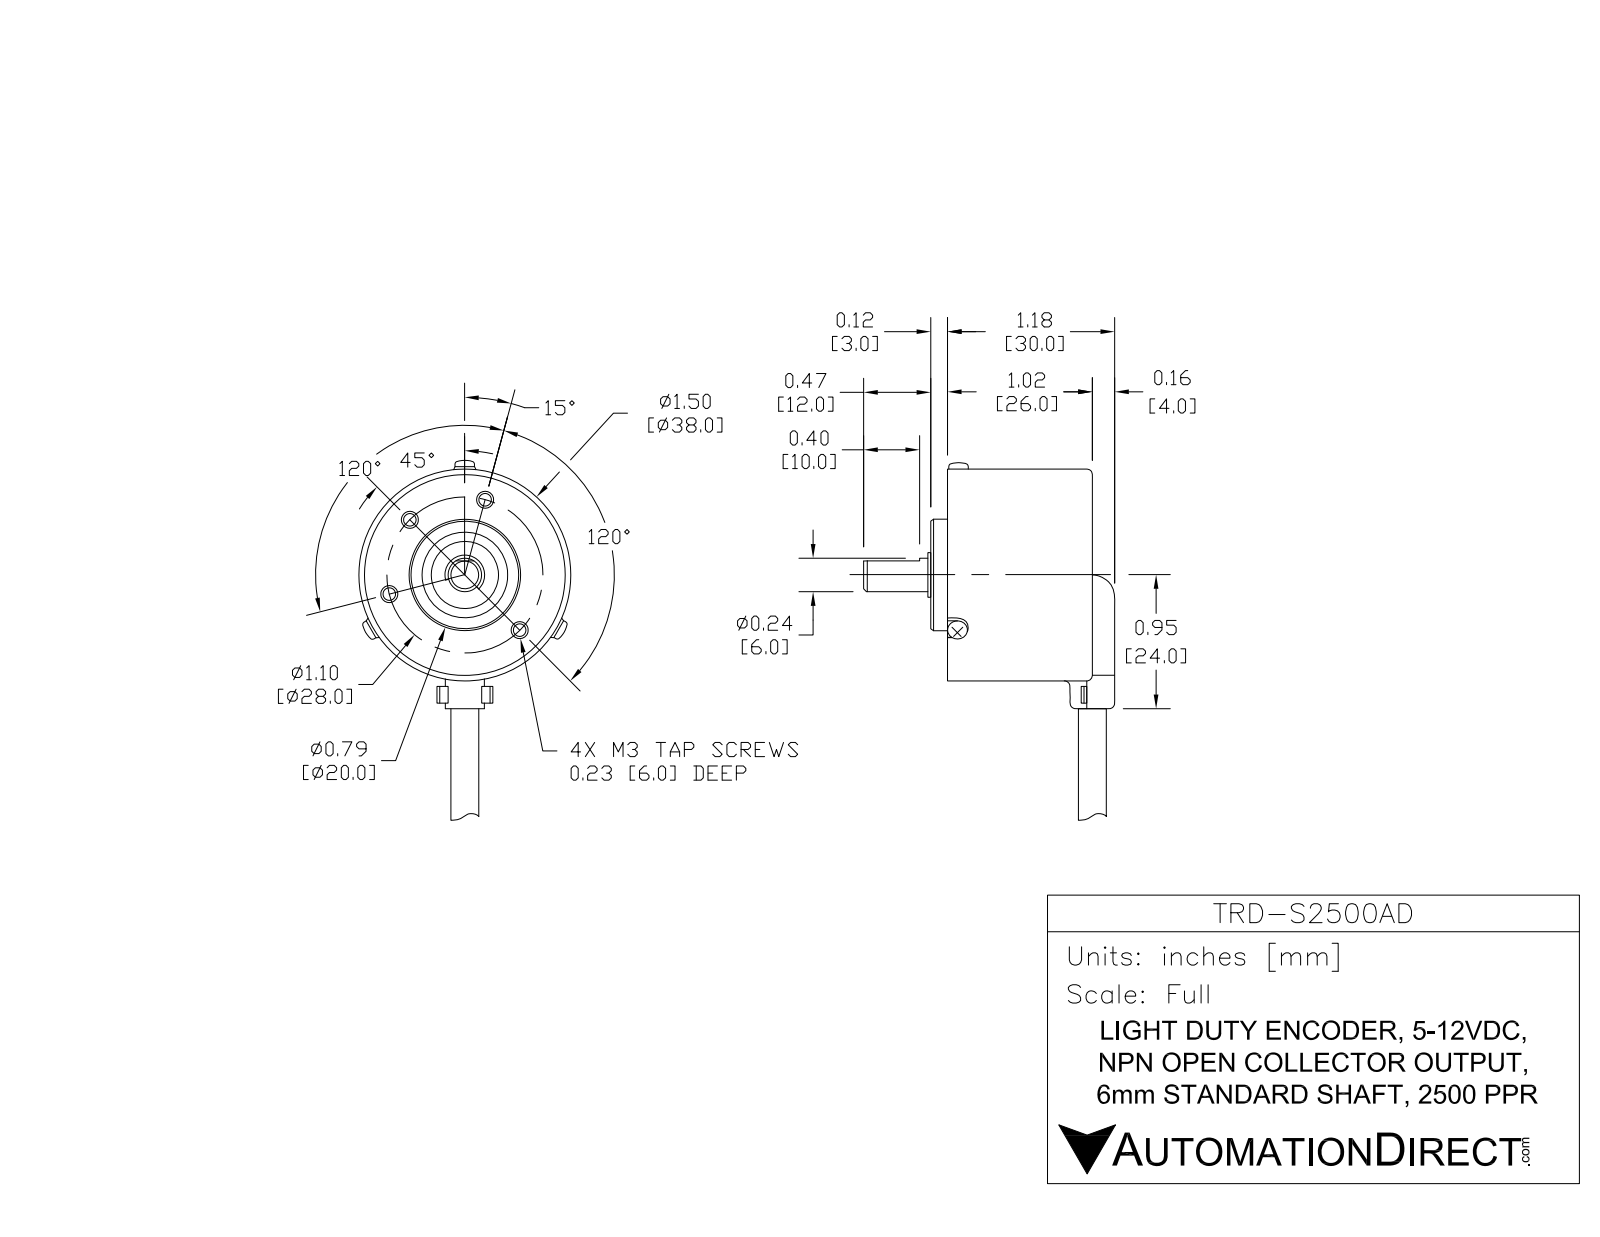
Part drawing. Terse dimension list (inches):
name: TRD-S2500AD
written by: SolidWorks 2016 (AUTOMOTIVE_DESIGN)
unit: in
bodies: 3 solids, 257 faces (98 planar, 100 cylindrical, 59 other)
size: 7.189 × 1.768 × 1.496
volume: 2.068 in³; area: 13.85 in²
holes: 4× ⌀0.118, 1× ⌀0.205, 1× ⌀0.256, 1× ⌀1.409
bosses: 1× ⌀1.496, 1× ⌀0.787, 1× ⌀0.591, 1× ⌀0.315, 1× ⌀0.236, 1× ⌀0.197, 1× ⌀0.193
rounds: 11× R0.016, 4× R0.004, 3× R0.13, 3× R0.748, 2× R0.008, 2× R0.02, 2× R0.146, 1× R0.11
face distances: 1.024, 0.118, 1.142, 0.02, 0.138, 0.803, 1.161, 0.354, 0.335, 0.217
hole spacings: 0.551, 0.955, 0.954, 1.102
